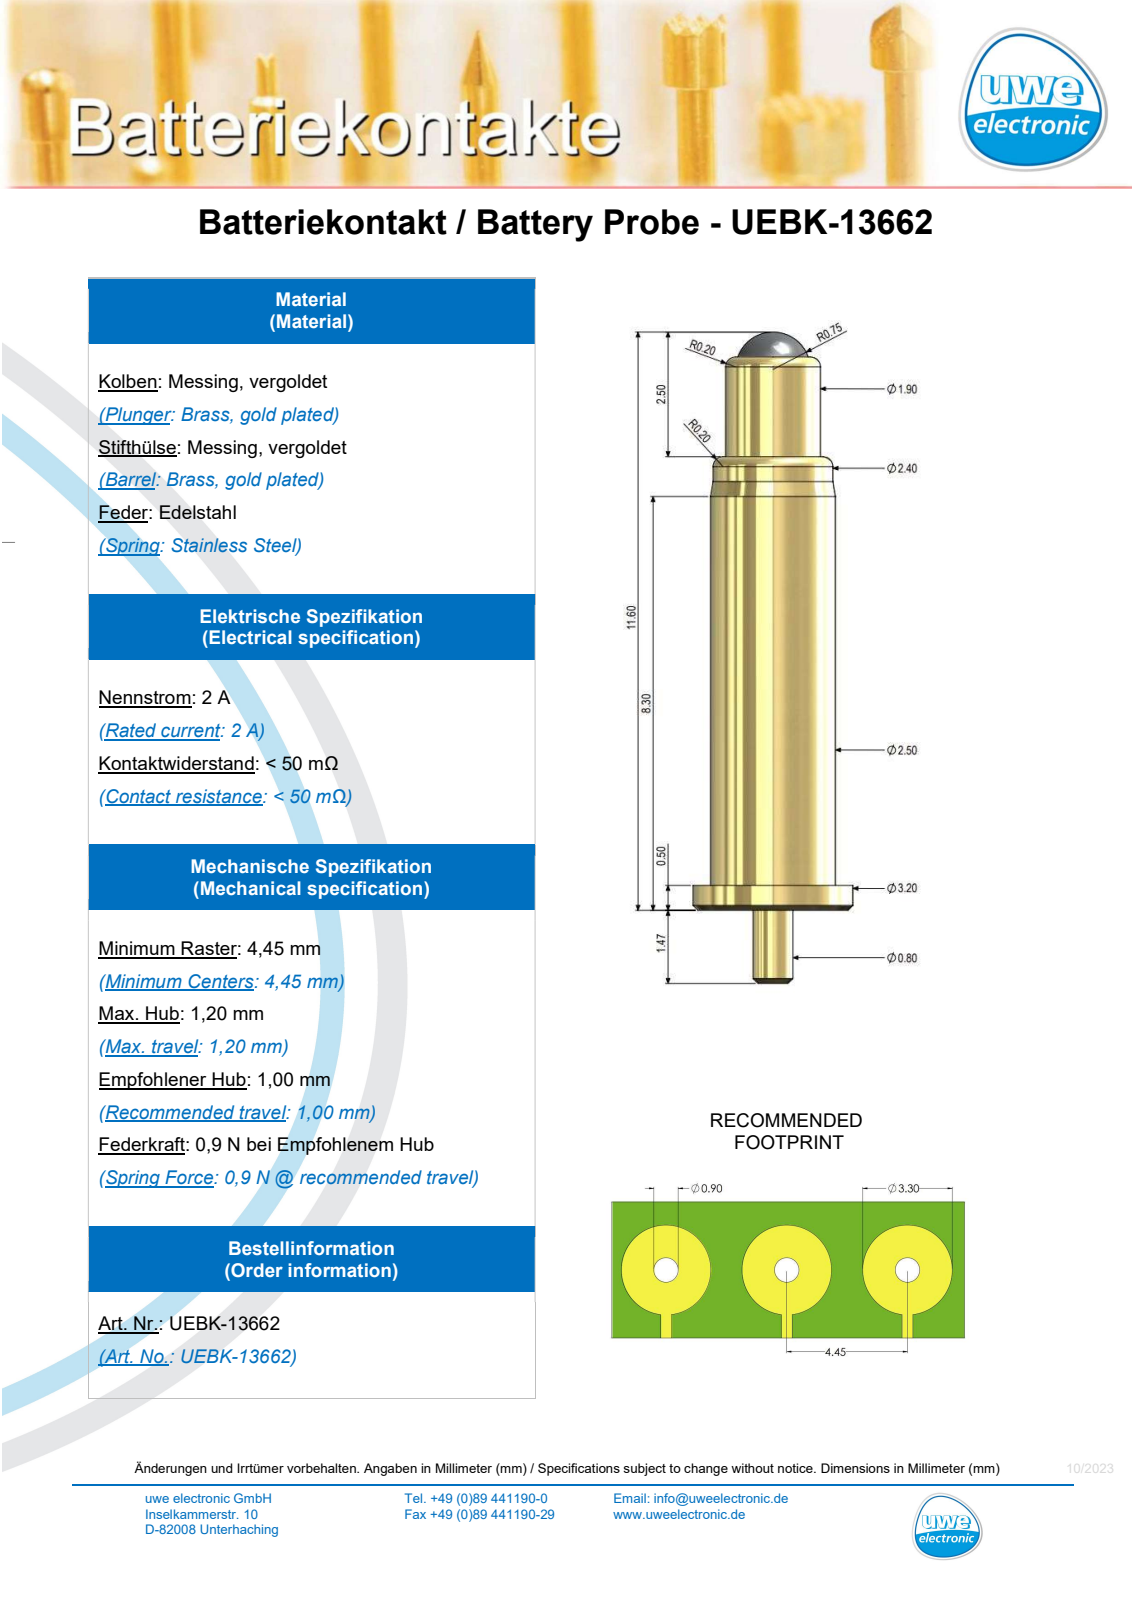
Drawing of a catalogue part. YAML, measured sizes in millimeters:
part_name: "UEBK-13662_step"
step_written_by: "SolidWorks 2022 (AUTOMOTIVE_DESIGN)"
units: millimeters
bodies: {solids: 1, faces: 26, planar: 5, cylindrical: 10, other: 11}
overall_size: [13.07, 3.2, 3.2]
volume: 53
surface_area: 103
round_bosses_or_shafts:
  - {diameter: 3.2, count: 1}
  - {diameter: 2.5, count: 1}
  - {diameter: 2.4, count: 1}
  - {diameter: 1.9, count: 1}
  - {diameter: 0.8, count: 1}
face_to_face_distances: [0.5, 9.1, 8.6, 1.47, 1.97, 10.57, 12.57, 11.1, 10.6, 2]
